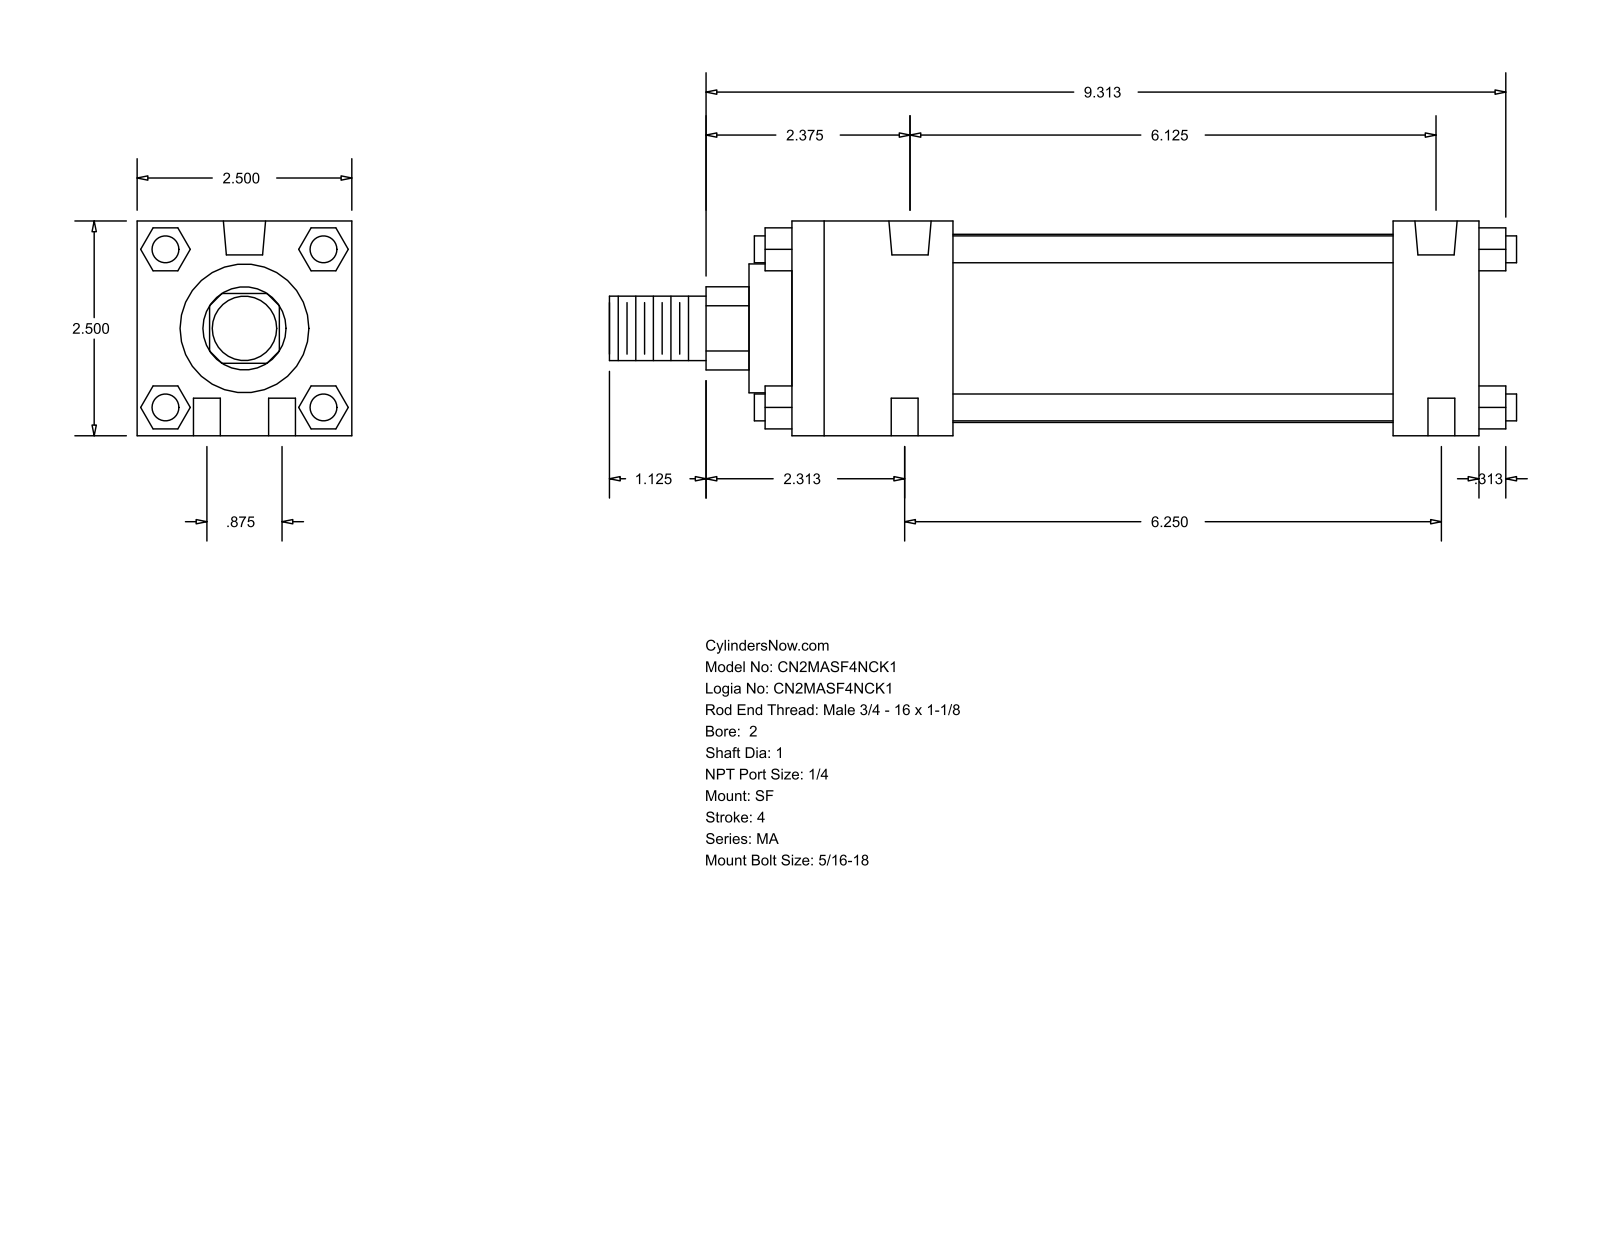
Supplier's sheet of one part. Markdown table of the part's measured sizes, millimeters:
| quantity | value |
| --- | --- |
| part name | MA_SF__0200_1 |
| STEP written by | GSSL Pune (CONFIG_CONTROL_DESIGN) |
| units | millimeters |
| bodies | 0 solids, 124 faces (94 planar, 30 cylindrical, 0 other) |
| overall size | 268.29 × 63.5 × 63.5 |
| round holes (diameter × count) | 7.94 × 6, 12.49 × 2 |
| round bosses / shafts (diameter × count) | 7.94 × 4, 55.63 × 1, 38.1 × 1, 25.4 × 1, 19.05 × 1 |
| partial cylindrical surfaces (radius × count) | 12.29 × 1 |
| main face-to-face distances | 63.5, 203.2, 12.7, 25.4, 177.8, 47.63, 130.17, 155.57, 23.37, 40.47 |
| hole center spacings | 11.22, 157.55, 22.22, 155.57, 158.75, 160.3 |
